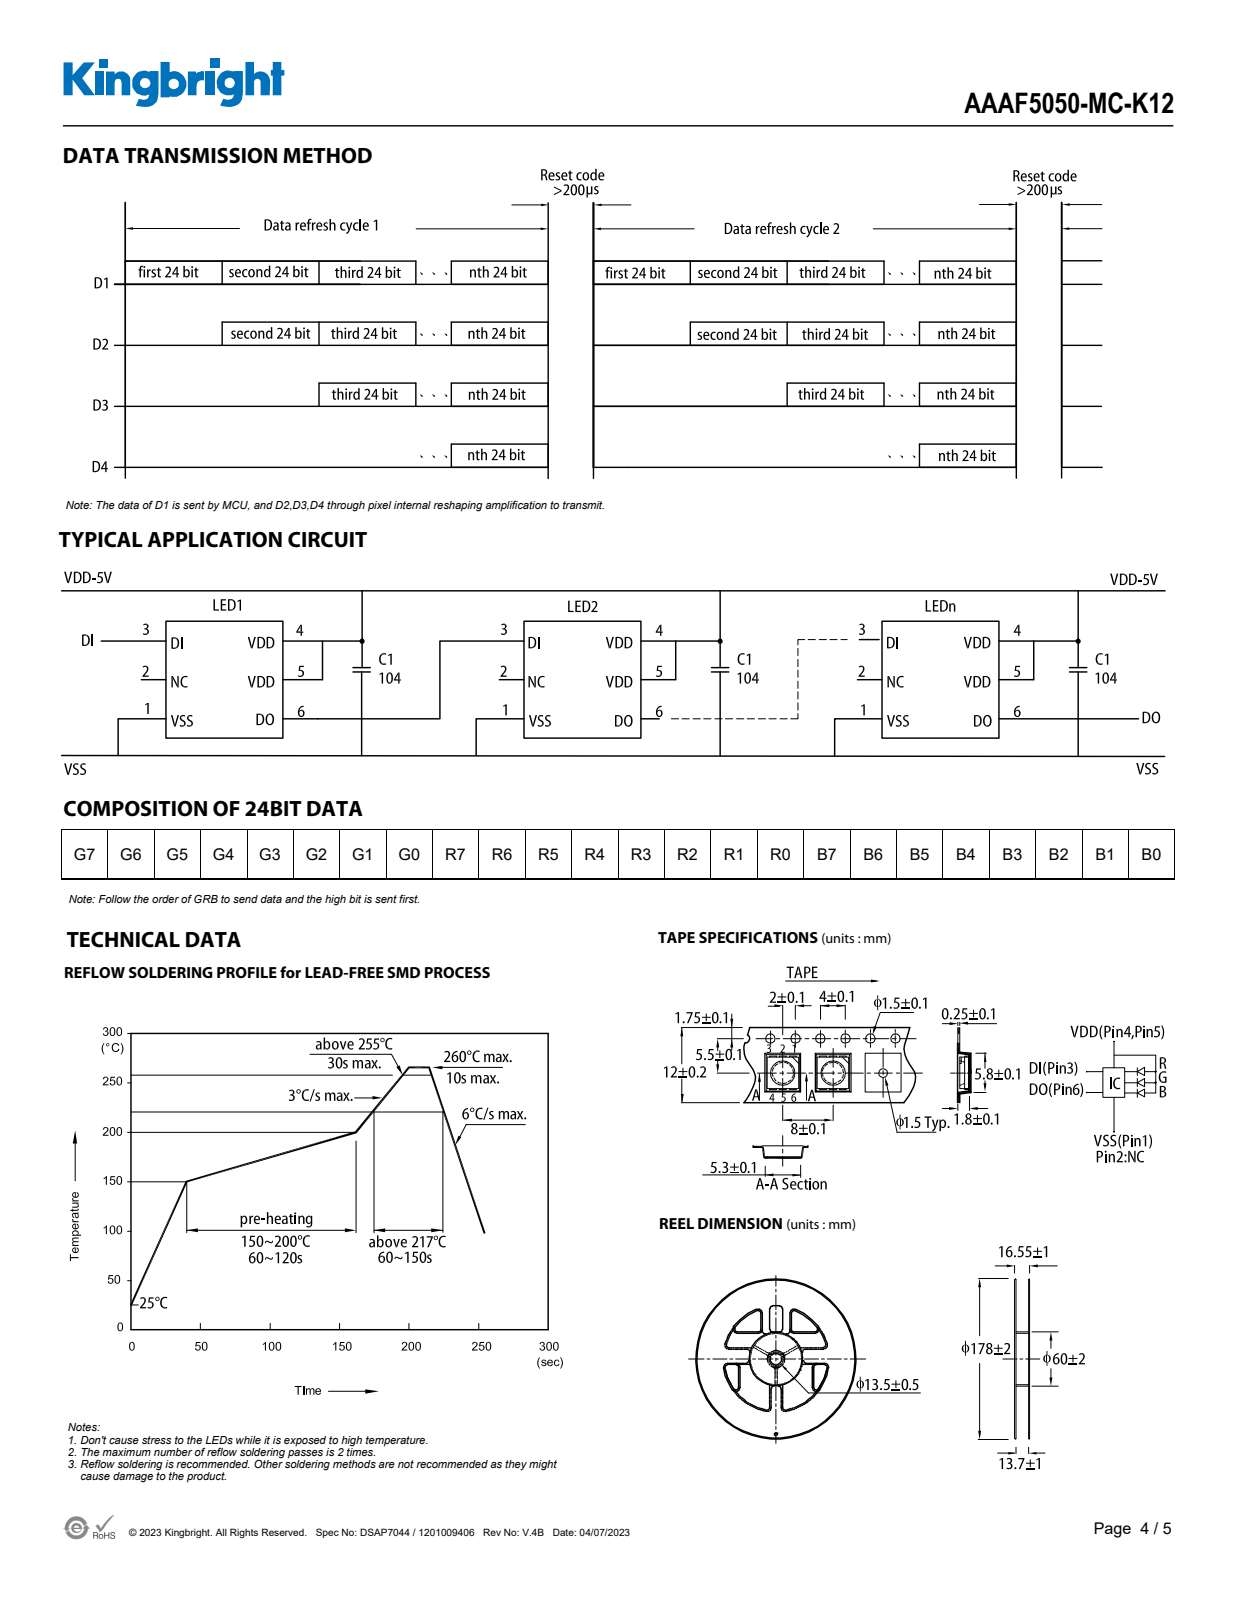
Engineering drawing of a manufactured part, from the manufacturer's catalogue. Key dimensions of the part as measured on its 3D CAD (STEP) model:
Part name (STEP PRODUCT): AAAF5050-MC-K12
STEP written by: SolidWorks 2014 (AUTOMOTIVE_DESIGN)
Units: millimetres
Bodies: 14 solids, 141 faces (116 planar, 19 cylindrical, 6 other)
Overall size (bounding box): 5.4 × 5 × 1.6
Volume: 40 mm³ · Surface area: 163 mm²
Round bosses / shafts (diameter × count): ⌀3.4 ×1
Partial cylindrical surfaces — rounded edges, fillets, slot ends (radius × count): R0.15 ×4
Main face-to-face distances: 0.8, 1.6, 0.6, 5, 0.58, 1.38, 0.82, 0.78, 0.77, 0.55
